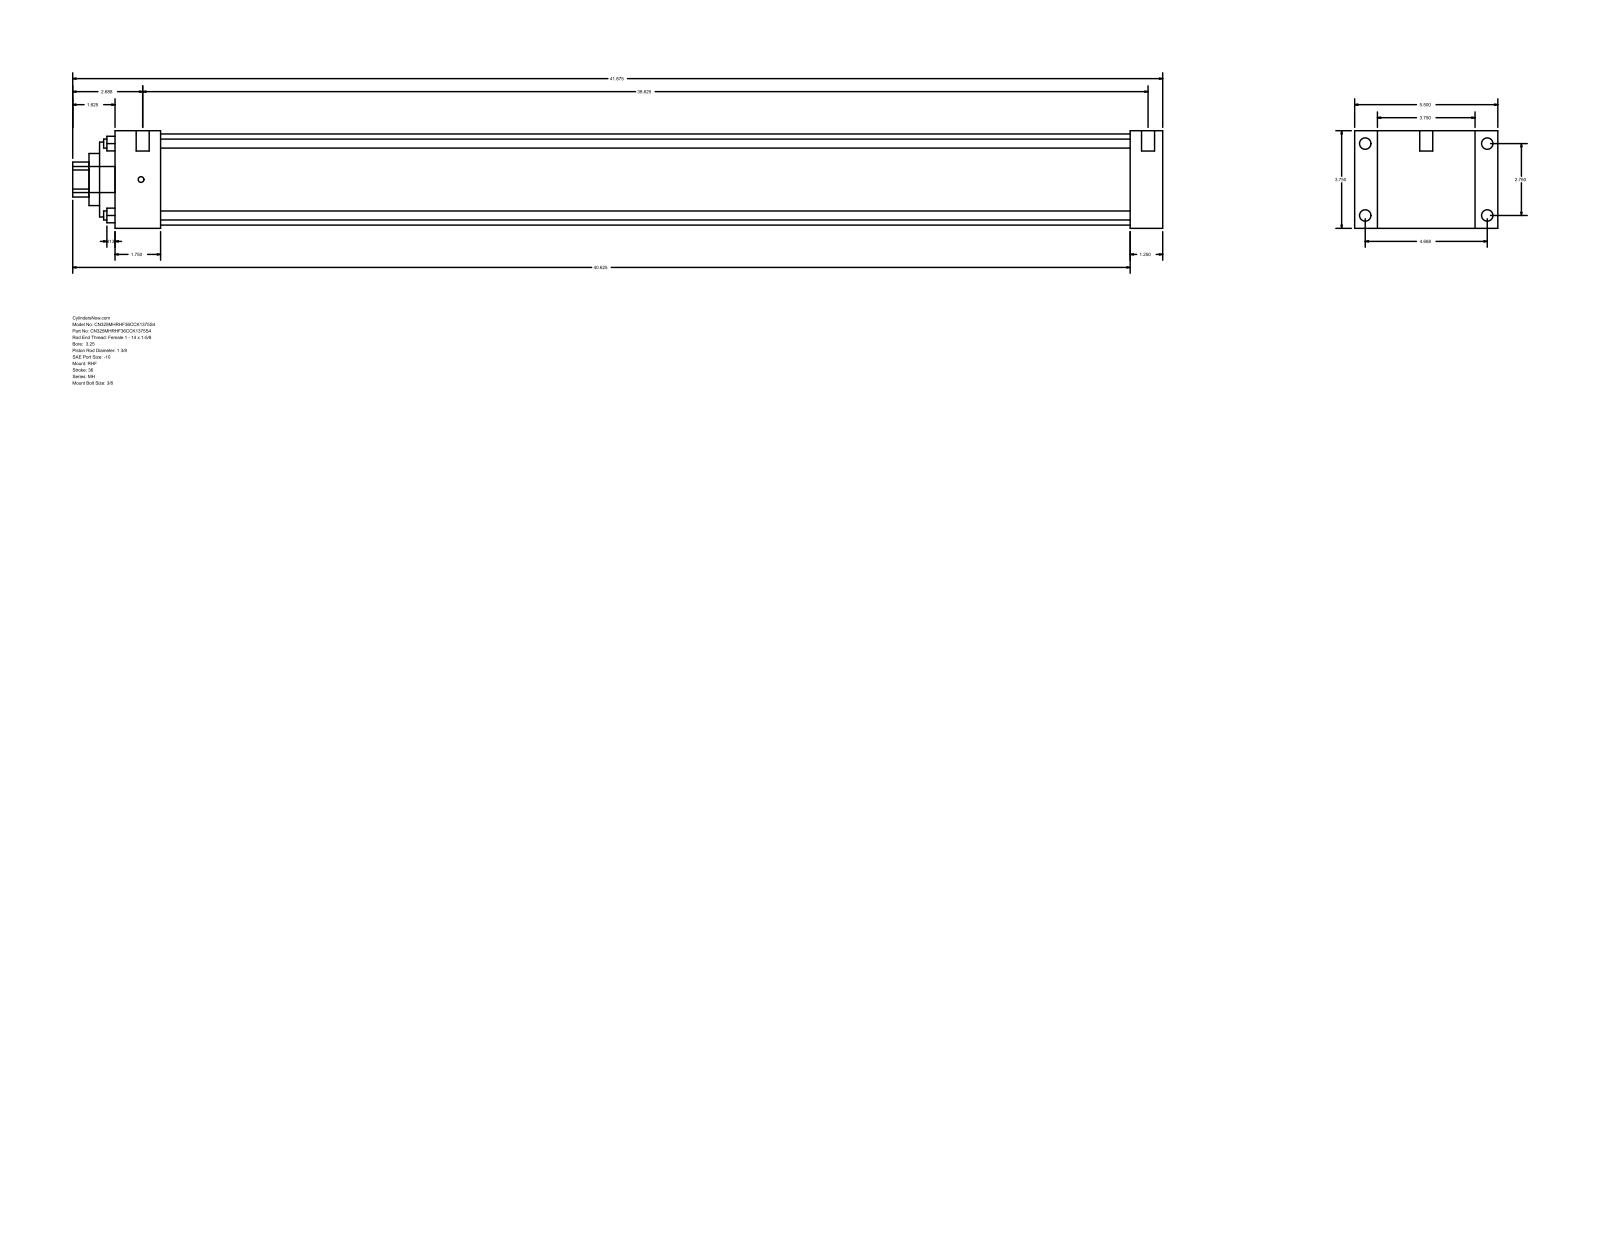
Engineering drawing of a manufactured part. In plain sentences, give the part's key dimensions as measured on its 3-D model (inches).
The part is named "MH_RHF__0325_1.375". Its 3-D file was written by "GSSL Pune (CONFIG_CONTROL_DESIGN)". It is 0 solids with 90 faces: 61 planar, 29 cylindrical and 0 other. Overall it measures 41.875 by 5.5 by 3.75 inches. Round holes: 4 of diameter 0.345, 1 of diameter 1.375, 1 of diameter 2, 1 of diameter 2.875, 1 of diameter 3.5. Round bosses or shafts: 4 of diameter 0.438, 4 of diameter 0.219, 2 of diameter 0.5, 1 of diameter 1. Partial cylindrical surfaces (rounded edges, fillets, slot ends): 1 of radius 0.672. The main face-to-face distances are 3.75, 1.25, 0.875, 4.625, 39, 40.25, 5.5, 1.75, 37.25, 38.5. The hole center spacings are 1.952, 2.76, 3.903.
